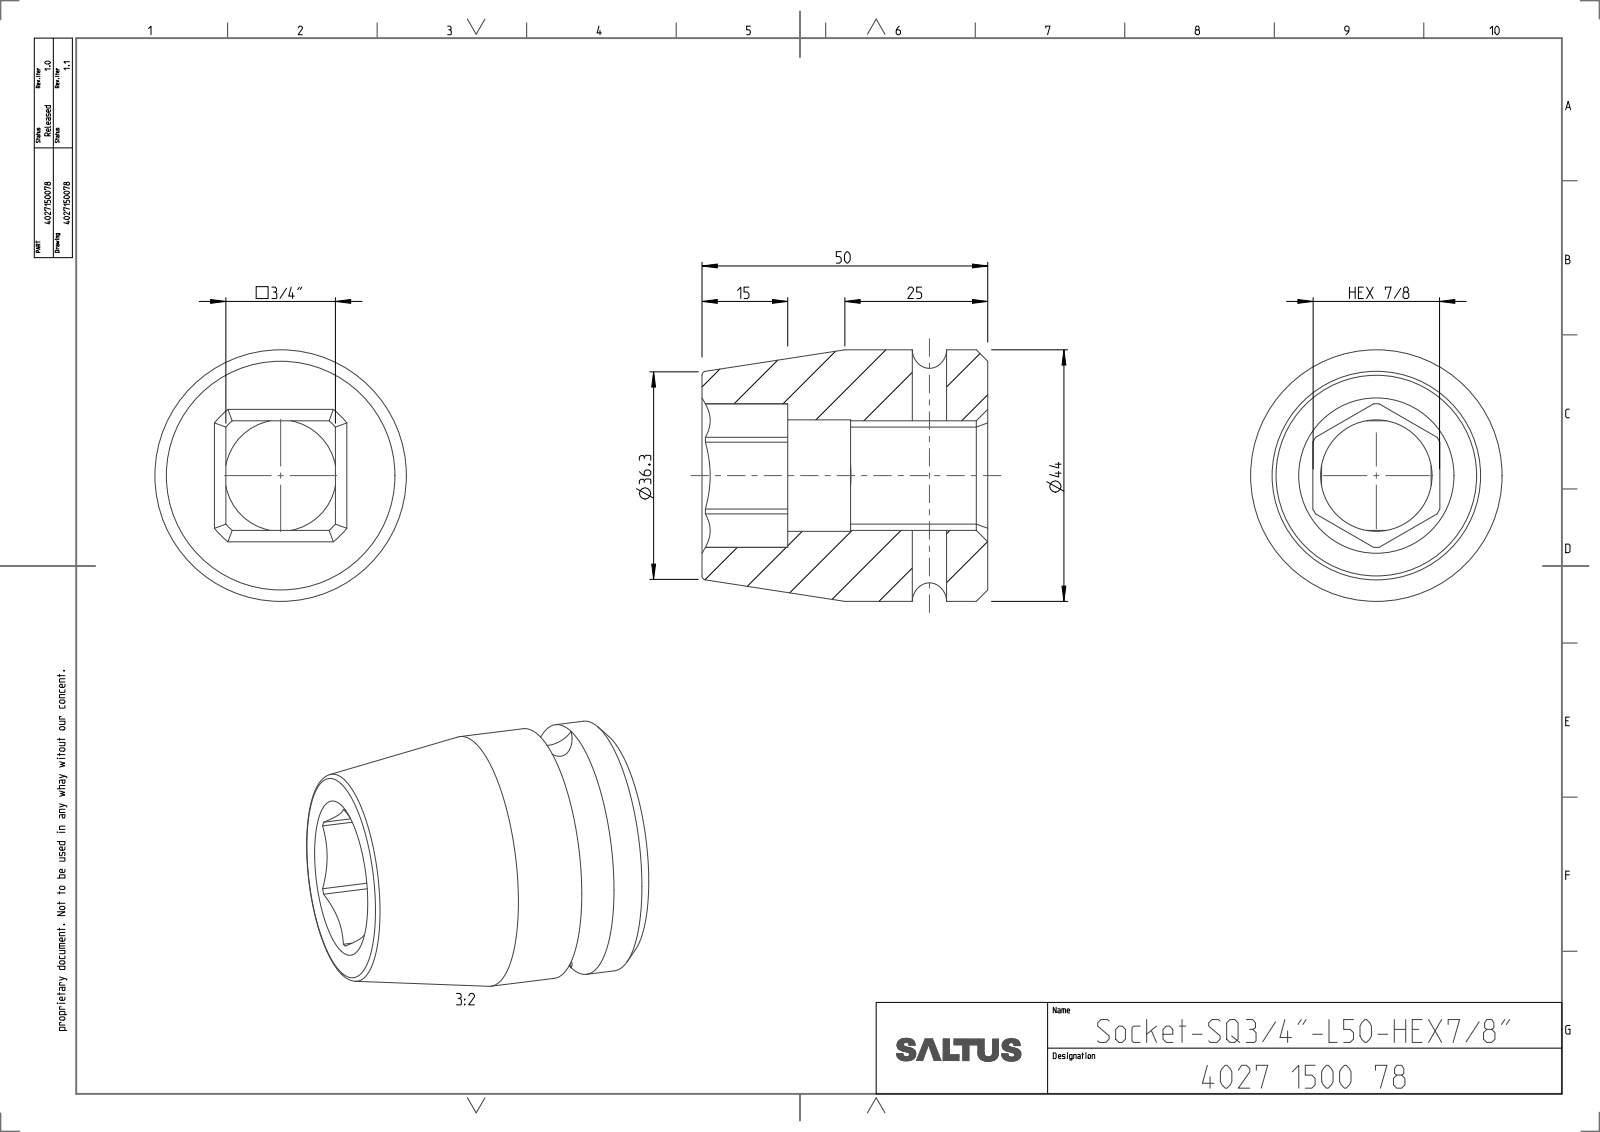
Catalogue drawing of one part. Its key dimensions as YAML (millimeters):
part_name: "4027150078"
step_written_by: "CREO PARAMETRIC BY PTC INC, 2022414 (CONFIG_CONTROL_DESIGN)"
units: millimeters
bodies: {solids: 1, faces: 59, planar: 21, cylindrical: 20, other: 18}
overall_size: [50, 44, 44]
volume: 48392
surface_area: 12491
round_holes:
  - {diameter: 6, count: 1}
  - {diameter: 19.5, count: 1}
round_bosses_or_shafts:
  - {diameter: 44, count: 1}
partial_cylinders:
  - {radius: 12.56, count: 1}
  - {radius: 12.8, count: 1}
face_to_face_distances: [19.18, 22.22, 50, 1.52, 20.7, 35, 15, 24, 11, 26]
